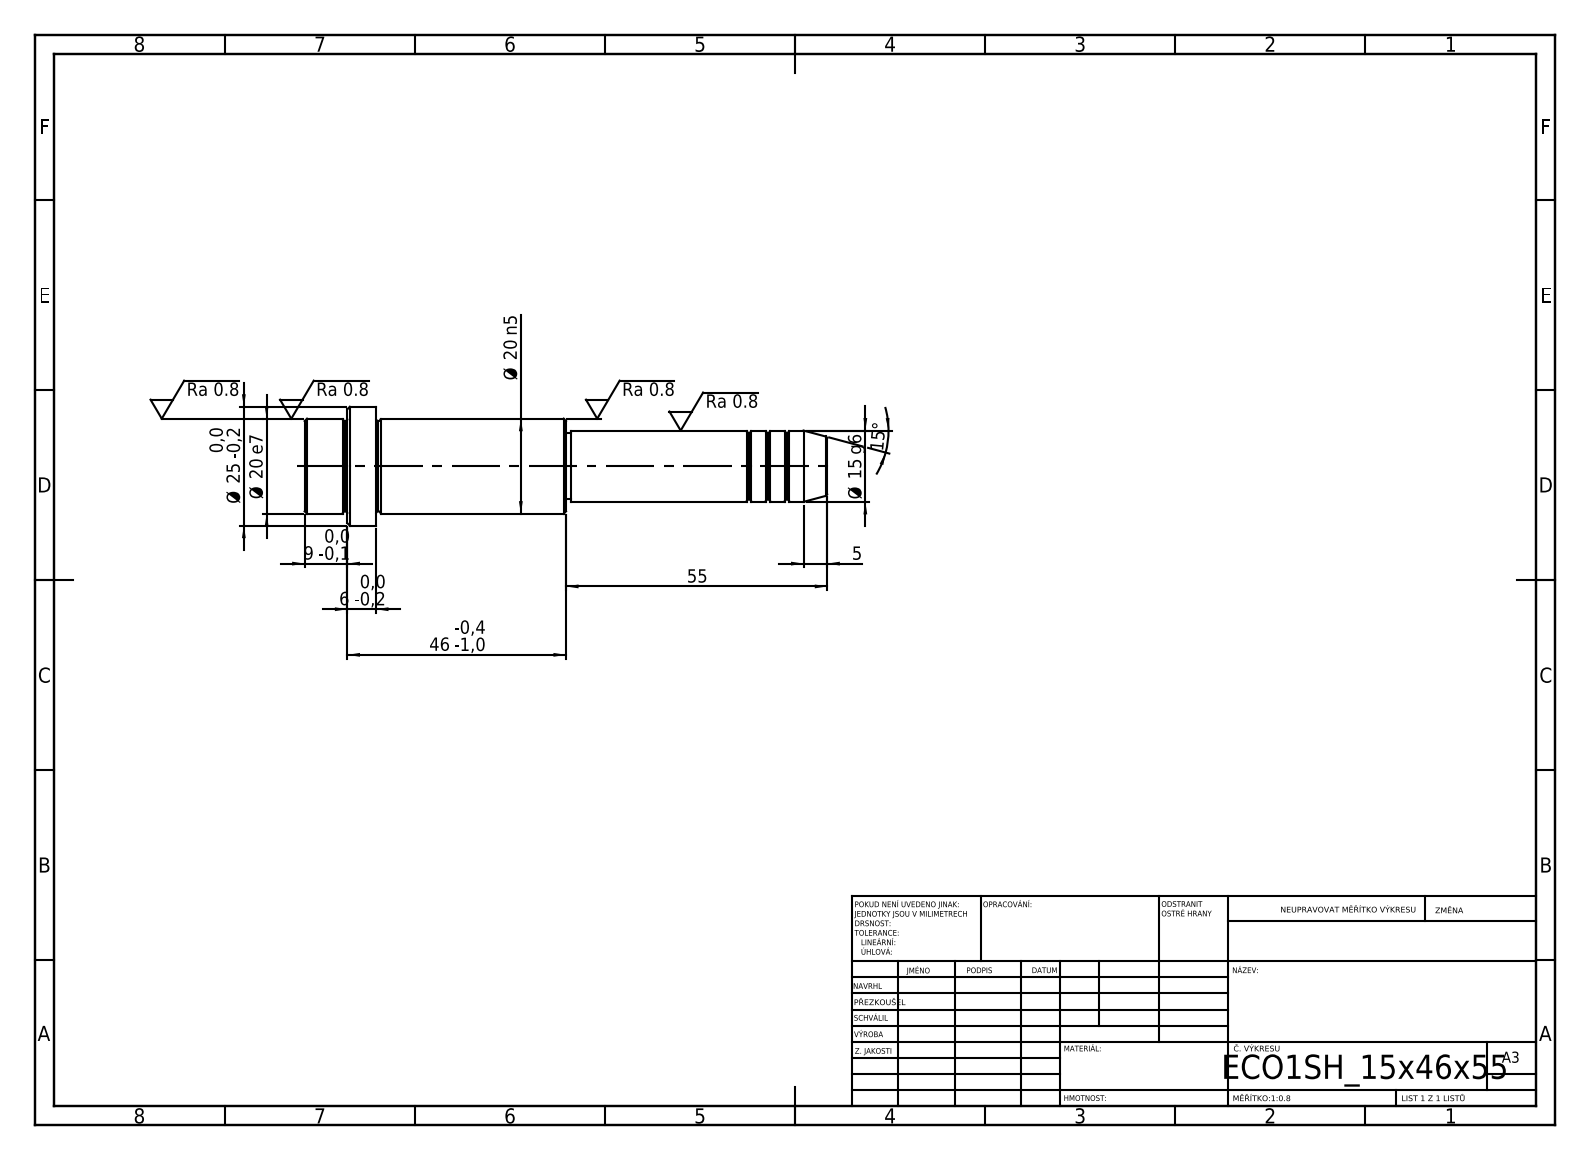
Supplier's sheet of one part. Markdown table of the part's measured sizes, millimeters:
| quantity | value |
| --- | --- |
| STEP written by | SolidWorks 2019 (CONFIG_CONTROL_DESIGN) |
| units | millimeters |
| bodies | 1 solid, 52 faces (6 planar, 16 cylindrical, 30 other) |
| overall size | 110 × 25 × 25 |
| volume | 27 759 mm³ |
| surface area | 7 166 mm² |
| round bosses / shafts (diameter × count) | 25 × 1, 20 × 1, 15 × 1, 14 × 1 |
| main face-to-face distances | 55, 15, 6, 9, 40, 46, 95, 101, 110, 54 |
